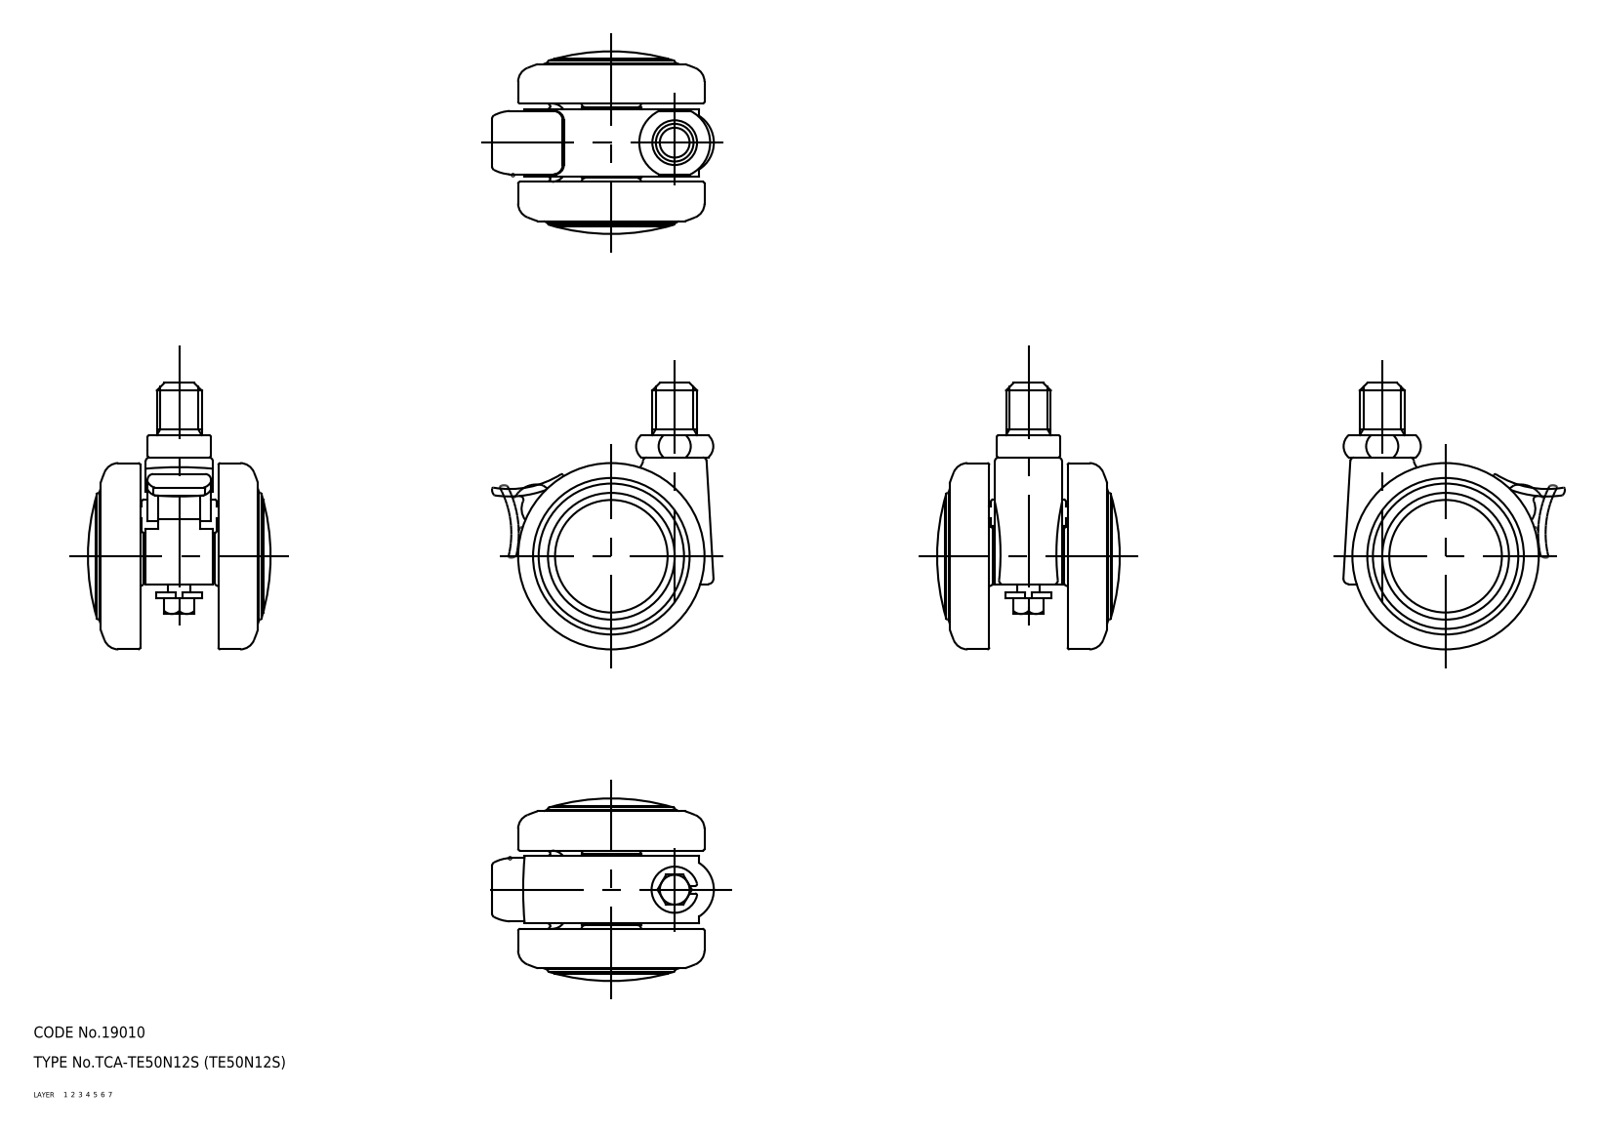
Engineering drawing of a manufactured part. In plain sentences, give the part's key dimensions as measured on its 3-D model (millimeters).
The part is named "wheel; main shaft; lever; TE50N12S_3304_36". Its 3-D file was written by "CADfix (AUTOMOTIVE_DESIGN)". It is 5 solids with 231 faces: 0 planar, 0 cylindrical and 231 other. Overall it measures 71.5 by 59.42 by 49 millimeters. Its volume is 63 721 cubic millimeters and its surface area 27 601 square millimeters.
